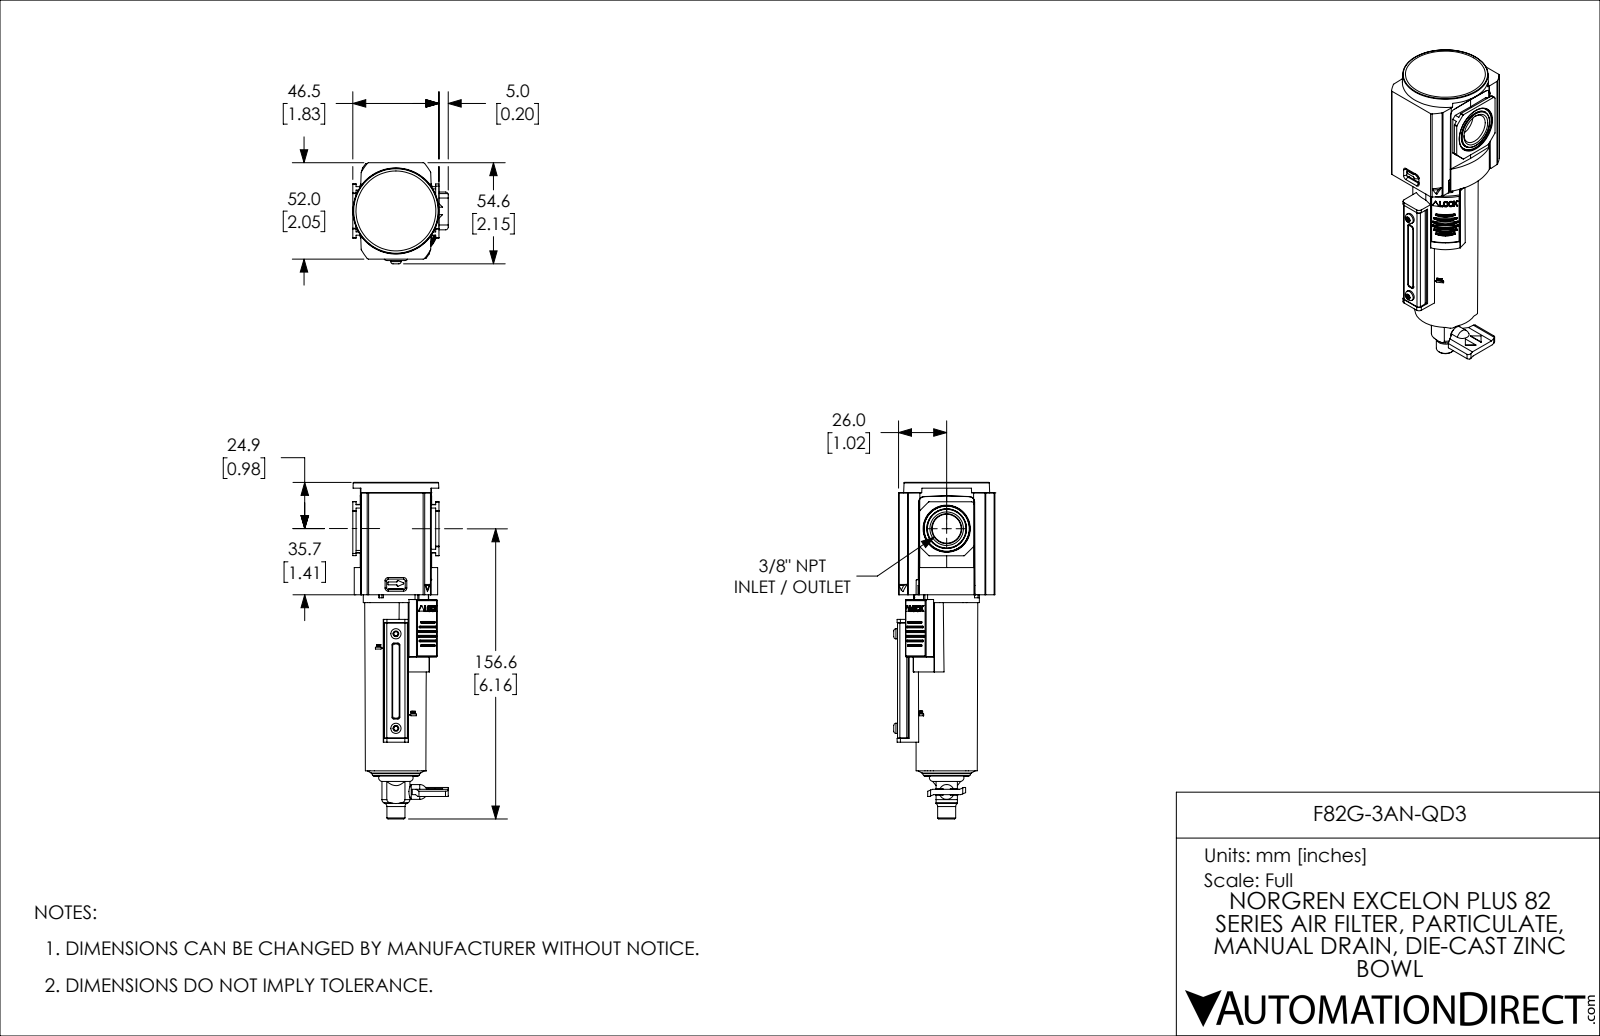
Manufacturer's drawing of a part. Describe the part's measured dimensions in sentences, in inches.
The part is named "F82G-3AN-QD3". Its 3-D file was written by "SolidWorks 2021 (CONFIG_CONTROL_DESIGN)". It is 5 solids with 1127 faces: 498 planar, 416 cylindrical and 213 other. Overall it measures 7.149 by 2.148 by 2.027 inches. Its volume is 12.81 cubic inches and its surface area 92.06 square inches. Round holes: 2 of diameter 0.128, 1 of diameter 0.25, 1 of diameter 0.628. Round bosses or shafts: 2 of diameter 0.217, 1 of diameter 1.388, 1 of diameter 1.356, 1 of diameter 1.291, 1 of diameter 1.257, 1 of diameter 0.906, 1 of diameter 0.626, 1 of diameter 0.383. Partial cylindrical surfaces (rounded edges, fillets, slot ends): 54 of radius 0.02, 45 of radius 0.039, 12 of radius 0.011, 12 of radius 0.019, 10 of radius 0.01, 8 of radius 0.031, 8 of radius 0.036, 8 of radius 0.048. The main face-to-face distances are 0.059, 1.988, 1.467, 2.047, 1.929, 0.058, 2.093, 2.151, 0.182, 0.236. The hole center spacings are 0.594, 1.189.
